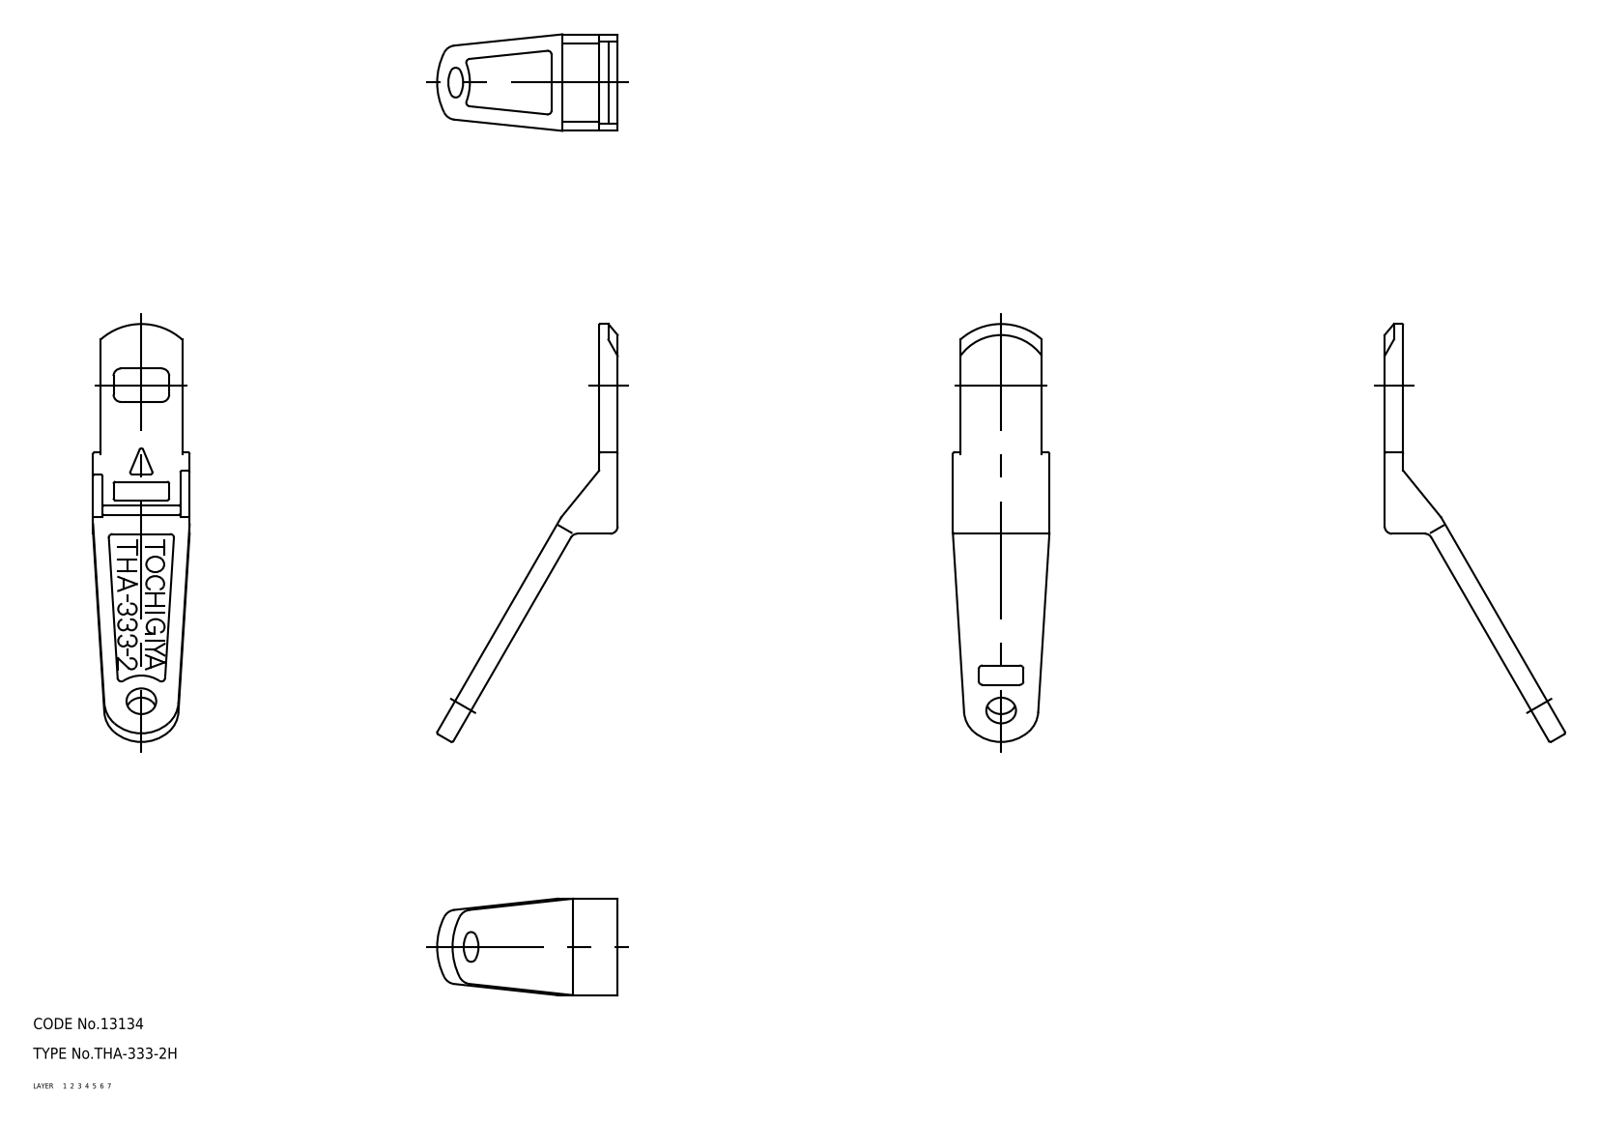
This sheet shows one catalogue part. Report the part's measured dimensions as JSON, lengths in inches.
{"part_name": "key_handle", "step_written_by": "CADfix (AUTOMOTIVE_DESIGN)", "units": "inches", "bodies": {"solids": 1, "faces": 97, "planar": 0, "cylindrical": 0, "other": 97}, "overall_size": [4.433, 1.915, 1.024], "volume_in3": 0.886, "surface_area_in2": 11.72}
